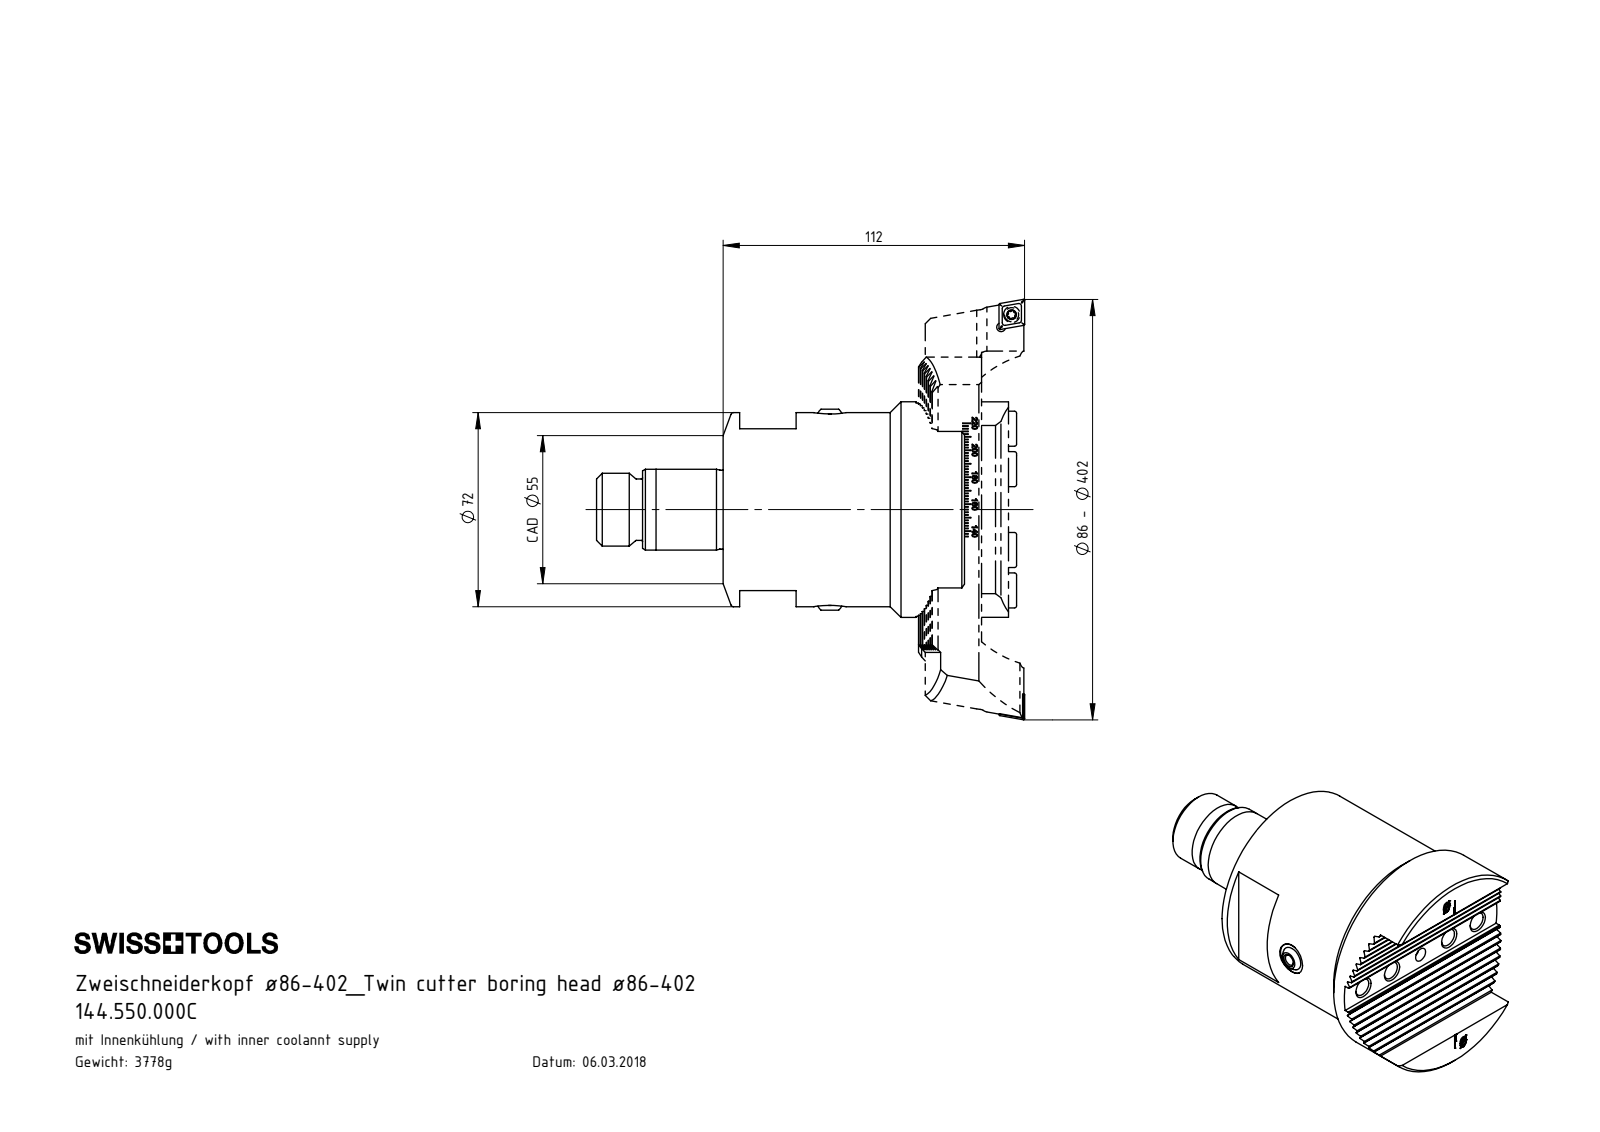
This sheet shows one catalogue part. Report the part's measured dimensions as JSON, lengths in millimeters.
{"part_name": "KU1-U12.001.010_2; CA5-Z00.K21.112_B; CCMT09T304; WCB-ER2.001.009_A (+7 more)", "step_written_by": "SolidWorks 2017 (CONFIG_CONTROL_DESIGN)", "units": "millimeters", "bodies": {"solids": 16, "faces": 1547, "planar": 871, "cylindrical": 192, "other": 484}, "overall_size": [158.89, 156, 80], "volume_mm3": 491766, "surface_area_mm2": 89290, "round_holes": [[3.3, 4], [6.8, 4], [8.5, 4], [14, 4], [4.4, 2], [6.1, 2], [2.5, 1], [4.2, 1], [5, 1], [7, 1], [10.2, 1], [12, 1]], "round_bosses_or_shafts": [[13, 4], [8, 4], [5.25, 2], [4, 2], [80, 1], [72, 1], [30, 1], [29.95, 1]], "partial_cylinders_radius": [[0.2, 32], [0.34, 12], [0.59, 12], [40, 8], [0.8, 2]], "face_to_face_distances": [2.38, 4.76, 21.3, 33.7, 7.14, 9.53, 7.15, 12.4, 14.29, 11.91], "hole_center_spacings": [15, 30, 6.06, 6.2, 45, 140.01, 140.12, 144.7]}
